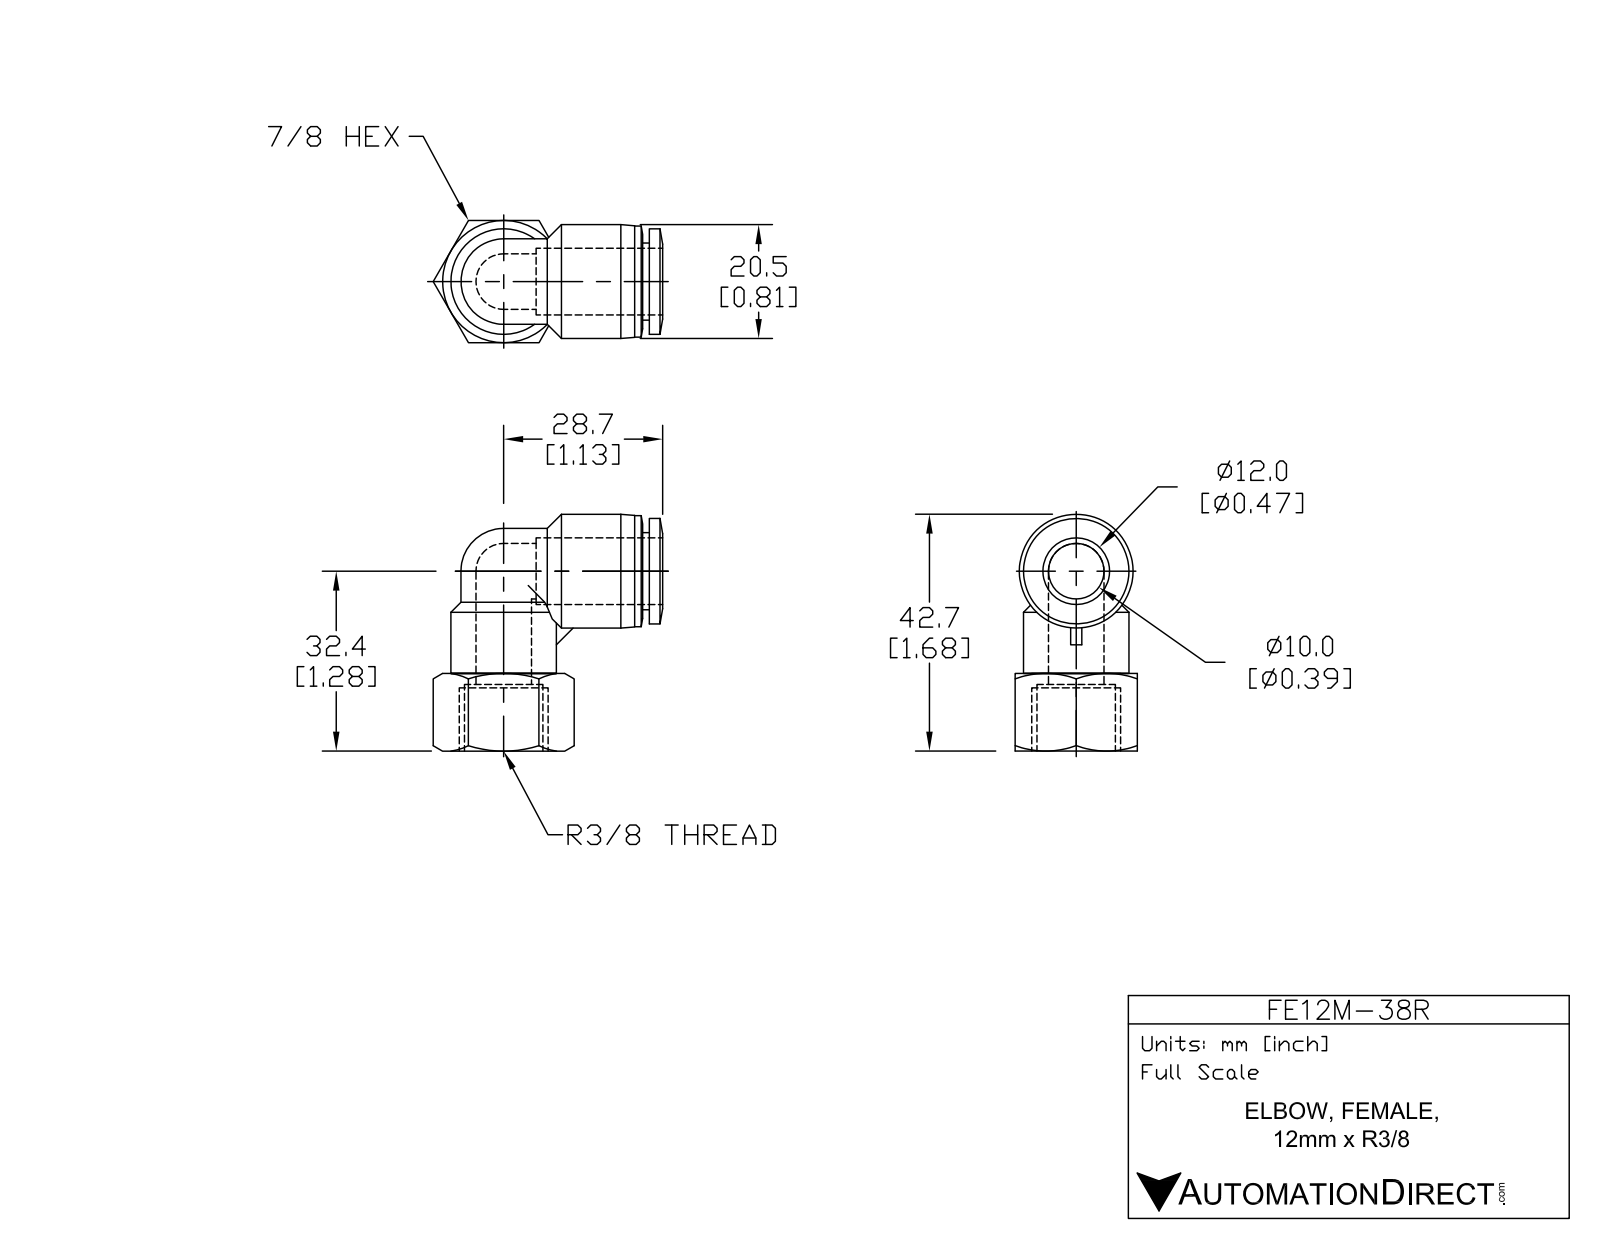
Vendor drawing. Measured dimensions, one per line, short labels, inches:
name: FE12M-38R
written by: SolidWorks 2015 (AUTOMOTIVE_DESIGN)
unit: in
bodies: 1 solid, 67 faces (17 planar, 19 cylindrical, 31 other)
size: 1.679 × 1.628 × 0.866
volume: 0.657 in³; area: 10.75 in²
holes: 2× ⌀0.394, 1× ⌀0.484
bosses: 2× ⌀0.748, 1× ⌀0.807, 1× ⌀0.787, 1× ⌀0.606, 1× ⌀0.547
rounds: 1× R0.303
face distances: 0.866, 0.472, 0.079, 0.551, 0.047, 0.76, 0.807, 0.902, 0.142, 0.094
